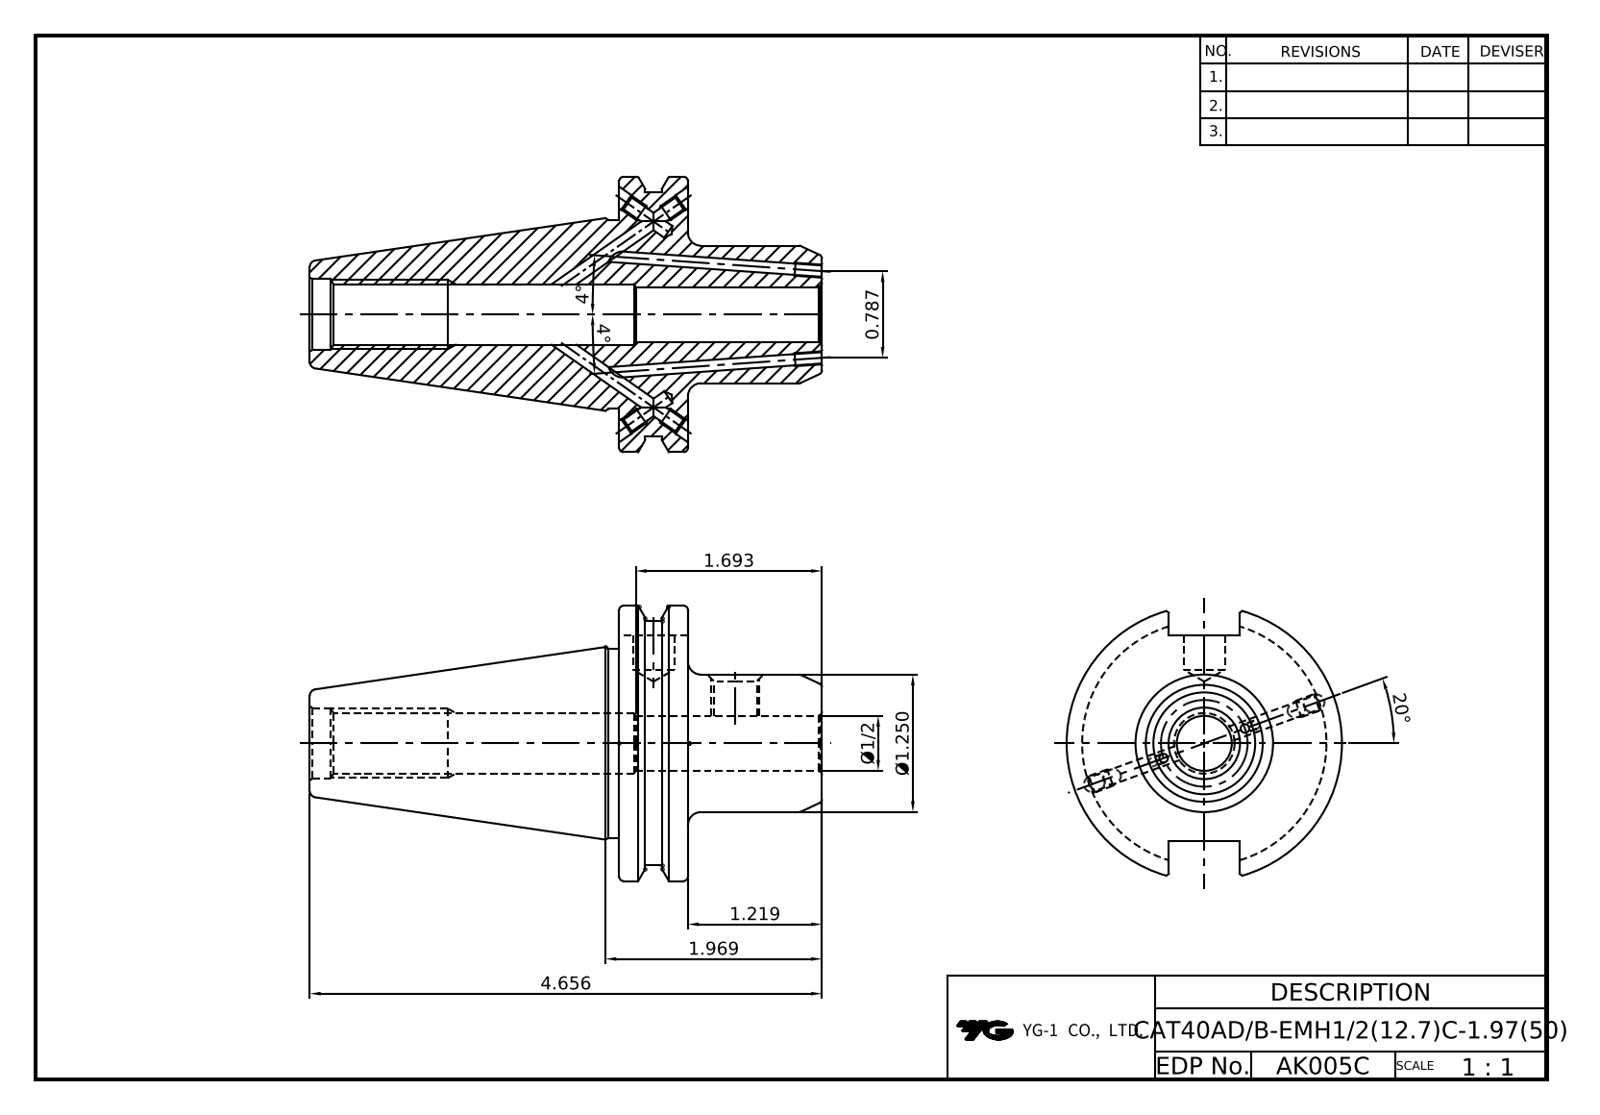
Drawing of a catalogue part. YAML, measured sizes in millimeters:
part_name: "CAT40ADB-EMH12_7C-50-PB15"
step_written_by: "CREO PARAMETRIC BY PTC INC, 2018400 (CONFIG_CONTROL_DESIGN)"
units: millimeters
bodies: {solids: 1, faces: 124, planar: 32, cylindrical: 48, other: 44}
overall_size: [118.25, 63.5, 61.09]
volume: 117552
surface_area: 26203
round_holes:
  - {diameter: 3.24, count: 4}
  - {diameter: 4, count: 4}
  - {diameter: 2.6, count: 2}
  - {diameter: 9.53, count: 1}
  - {diameter: 10, count: 1}
  - {diameter: 12.7, count: 1}
  - {diameter: 14, count: 1}
  - {diameter: 16.3, count: 1}
round_bosses_or_shafts:
  - {diameter: 63.5, count: 1}
  - {diameter: 56.3, count: 1}
  - {diameter: 43.6, count: 1}
  - {diameter: 31.8, count: 1}
face_to_face_distances: [15.88, 46.83, 30.95, 47.6, 16.38, 71.42, 87.3, 118.25, 3.83, 6.05]
hole_center_spacings: [35.13, 18.87]
